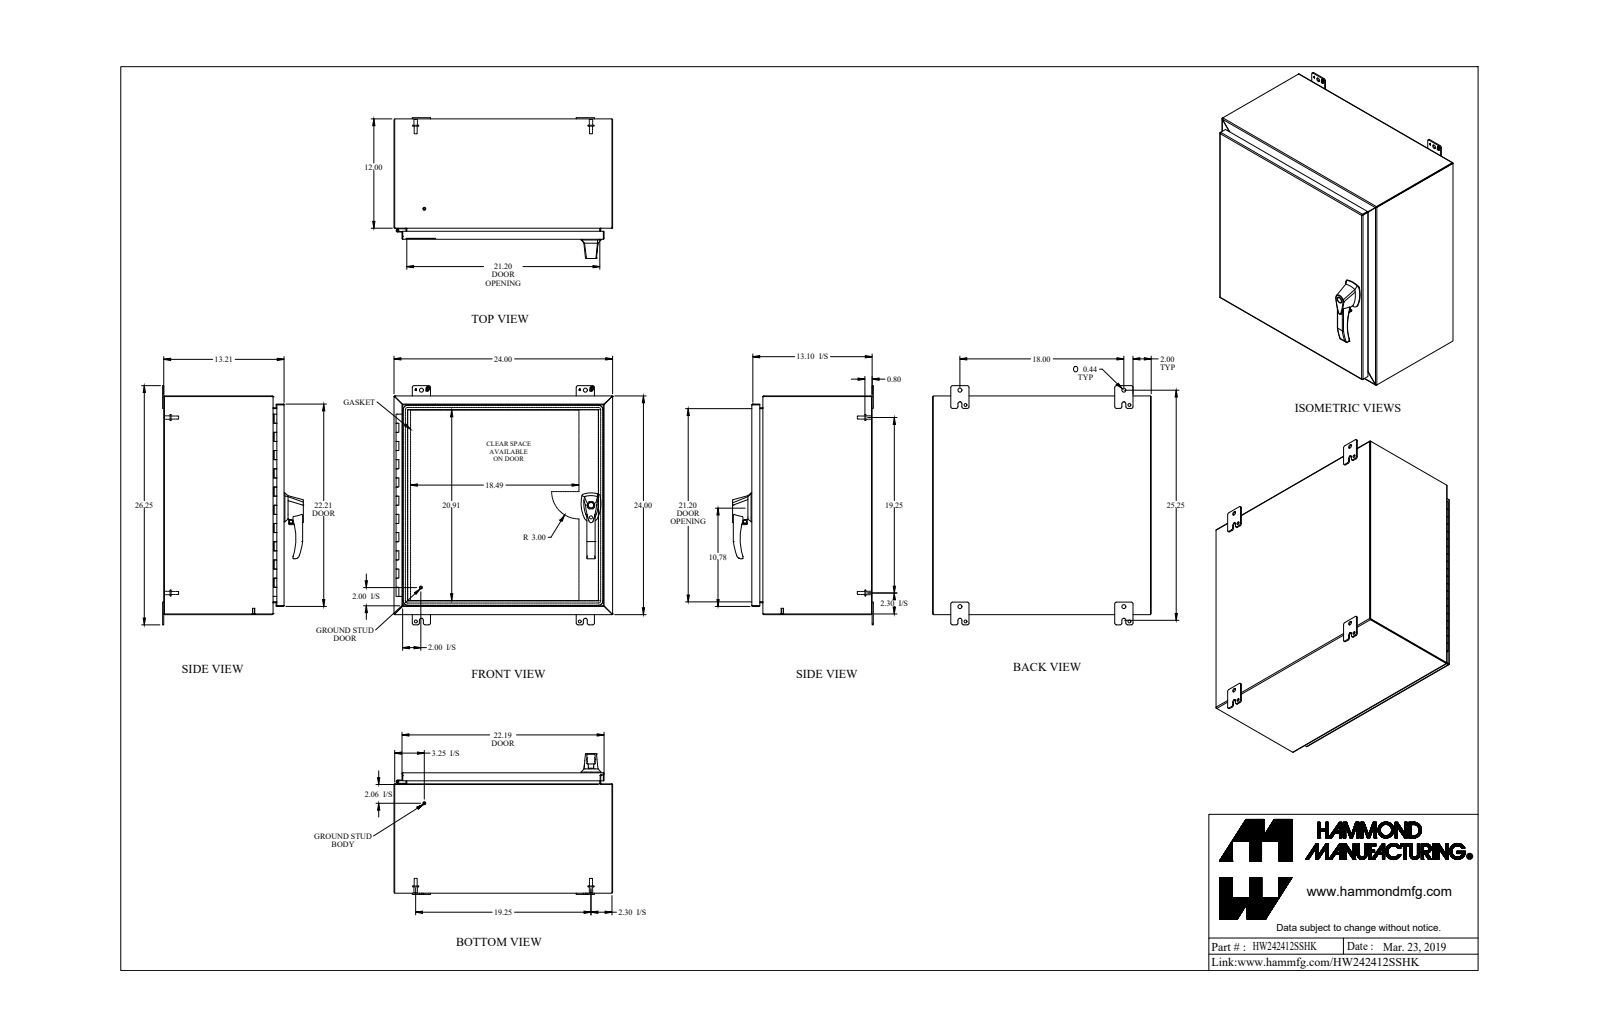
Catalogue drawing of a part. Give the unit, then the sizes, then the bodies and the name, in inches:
Units: inches
Overall size (bounding box): 26.25 × 24 × 15.45
Round holes (diameter × count): ⌀0.176 ×6, ⌀0.313 ×5, ⌀0.25 ×3, ⌀0.265 ×3, ⌀0.413 ×3, ⌀0.196 ×2, ⌀0.256 ×2, ⌀0.394 ×2, ⌀0.437 ×2, ⌀0.187 ×1, ⌀0.233 ×1, ⌀0.33 ×1
Round bosses / shafts (diameter × count): ⌀0.375 ×9, ⌀0.25 ×7, ⌀0.156 ×6, ⌀0.65 ×4, ⌀0.332 ×4, ⌀0.313 ×4, ⌀1 ×3, ⌀0.51 ×3
Partial cylindrical surfaces — rounded edges, fillets, slot ends (radius × count): R0.25 ×27, R0.188 ×24, R0.036 ×18, R0.108 ×18, R0.06 ×12, R0.125 ×9, R0.045 ×8, R0.218 ×8
Main face-to-face distances: 0.072, 23.928, 0.072, 23.856, 24, 13.138, 13.066, 13.138, 13.21, 11.928
Hole centre spacings: 1.11, 8.118, 8.119, 16.237, 1.338, 6.78, 7.576, 7.577
Volume: 215.1 in³ · Surface area: 5 572 in²
Bodies: 44 solids, 1371 faces (665 planar, 559 cylindrical, 147 other)
Part name (STEP PRODUCT): HW242412SSHK
STEP written by: SolidWorks 2018 (AUTOMOTIVE_DESIGN)
